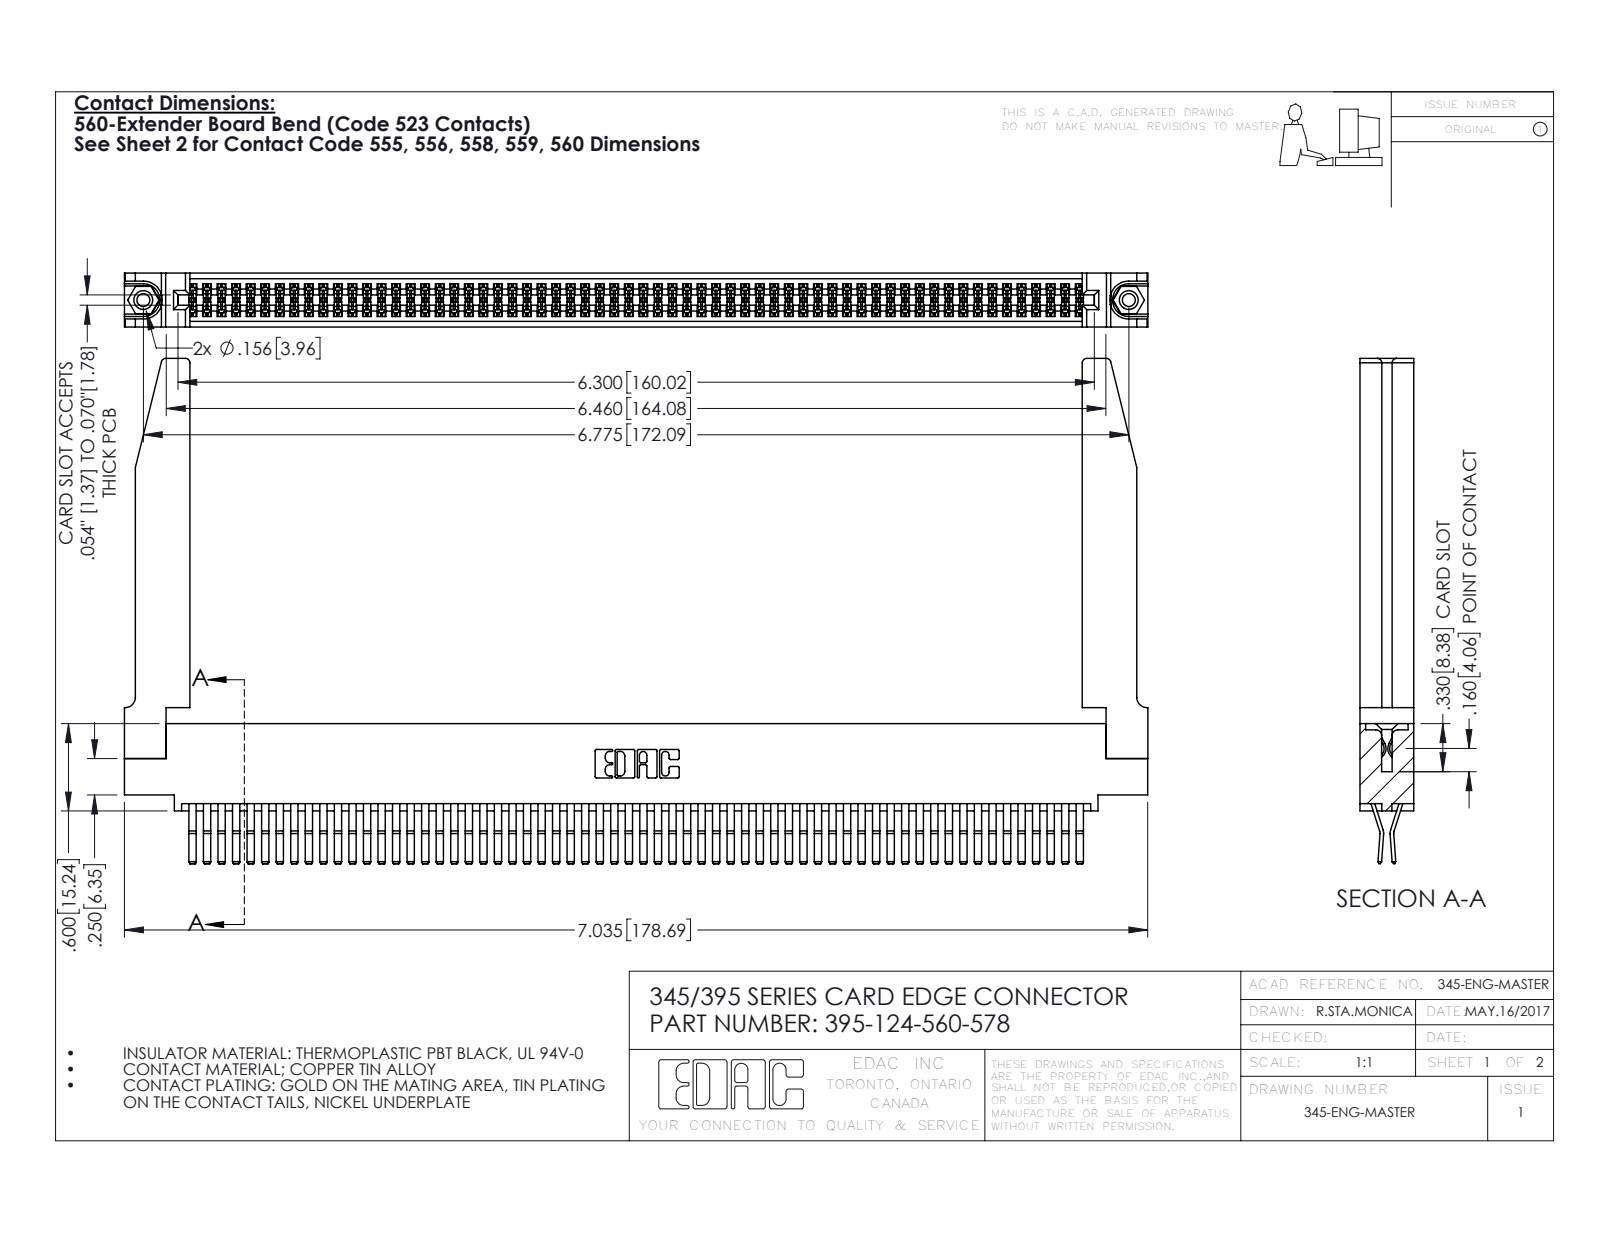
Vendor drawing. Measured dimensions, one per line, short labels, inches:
name: 345-292-001_560 Tail; 345-220-078_345-220-078; 395-124-560-578; 345 Part_0.110 Offset - 0.156 Dia-TH (+1 more)
written by: SolidWorks 2016 (CONFIG_CONTROL_DESIGN)
unit: in
bodies: 129 solids, 6812 faces (4318 planar, 2442 cylindrical, 52 other)
size: 7.036 × 3.472 × 0.37
volume: 1.59 in³; area: 56.48 in²
holes: 2× ⌀0.089, 2× ⌀0.125, 2× ⌀0.156, 1× ⌀0.064
bosses: 2× ⌀0.155
rounds: 187× R0.006, 22× R0.01, 8× R0.03, 6× R0.007, 6× R0.031, 3× R0.026, 2× R0.01, 2× R0.014
face distances: 0.072, 0.298, 0.025, 0.37, 0.098, 0.272, 0.2, 0.225, 0.175, 0.148
hole spacings: 0.27, 6.539, 6.775
